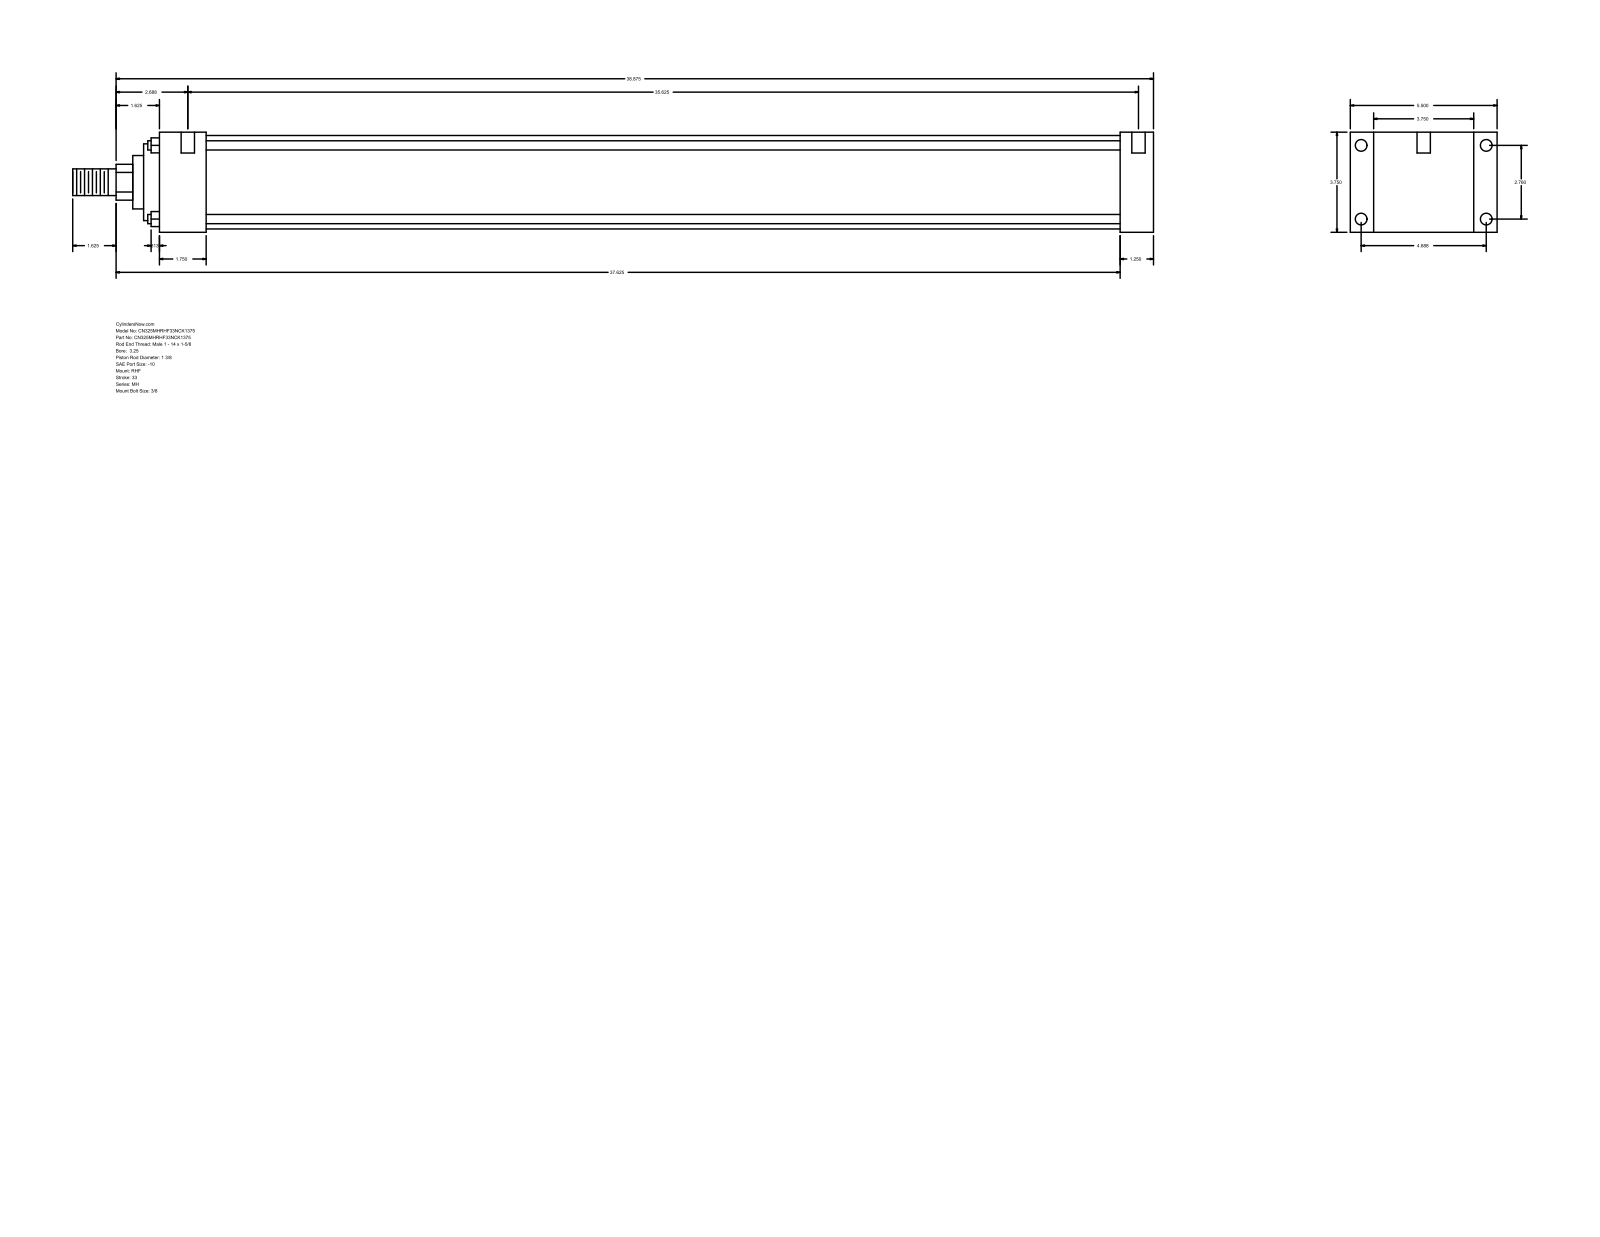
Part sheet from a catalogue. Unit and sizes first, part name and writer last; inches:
Units: inches
Overall size (bounding box): 40.5 × 5.5 × 3.75
Round holes (diameter × count): ⌀0.219 ×4, ⌀0.438 ×4, ⌀0.5 ×2
Round bosses / shafts (diameter × count): ⌀0.345 ×4, ⌀3.5 ×1, ⌀2.875 ×1, ⌀2 ×1, ⌀1.375 ×1, ⌀1 ×1
Partial cylindrical surfaces — rounded edges, fillets, slot ends (radius × count): R0.672 ×1
Main face-to-face distances: 3.75, 1.25, 0.875, 4.625, 36, 37.25, 5.5, 1.75, 34.25, 35.5
Hole centre spacings: 2.76, 4.687, 5.439, 35.875, 0.063, 0.187, 35.625, 35.688
Bodies: 0 solids, 90 faces (61 planar, 29 cylindrical, 0 other)
Part name (STEP PRODUCT): MH_RHF__0325_1.375
STEP written by: GSSL Pune (CONFIG_CONTROL_DESIGN)
